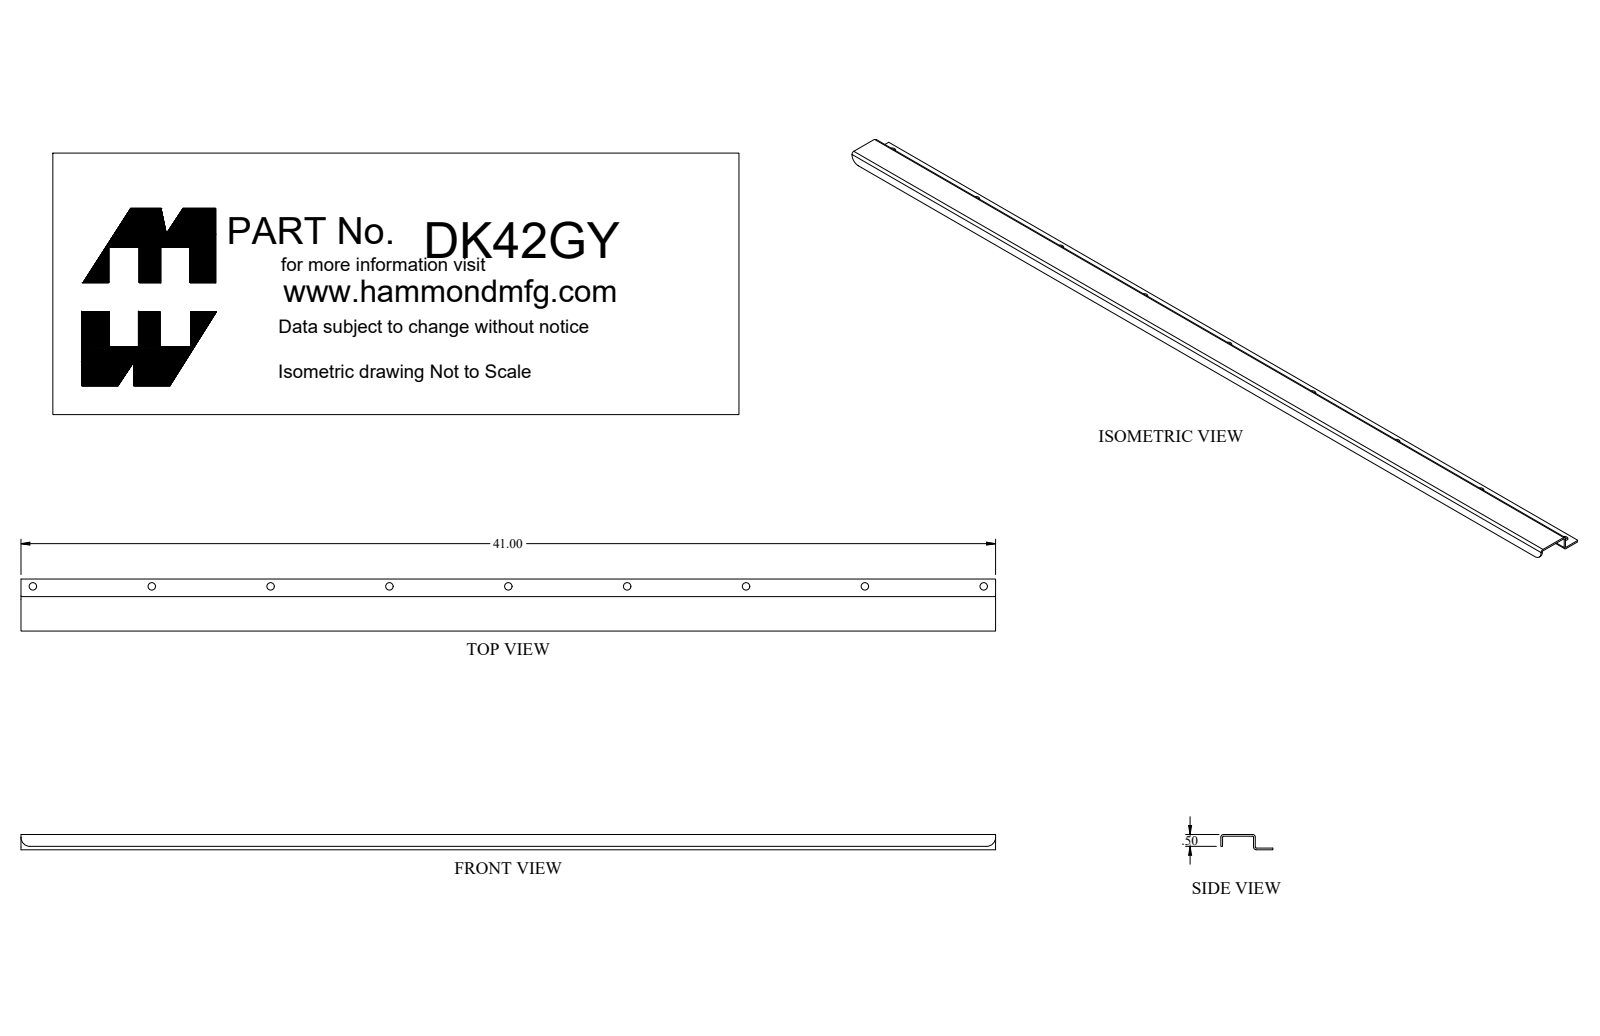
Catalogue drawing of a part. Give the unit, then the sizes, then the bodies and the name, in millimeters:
Units: millimetres
Overall size (bounding box): 1041.4 × 55.6 × 33.6
Round holes (diameter × count): ⌀8 ×9, ⌀5.1 ×1, ⌀7 ×1
Round bosses / shafts (diameter × count): ⌀15.9 ×1, ⌀12.3 ×1, ⌀6.4 ×1
Partial cylindrical surfaces — rounded edges, fillets, slot ends (radius × count): R0.9 ×3, R2.7 ×3, R9.5 ×2
Main face-to-face distances: 1.8, 14.5, 16.4, 35, 12.7, 1.6, 16.1, 18, 3.4, 36.8
Hole centre spacings: 127, 254, 381, 508, 635, 762, 889, 1016
Volume: 182 400 mm³ · Surface area: 212 100 mm²
Bodies: 5 solids, 77 faces (35 planar, 36 cylindrical, 6 other)
Part name (STEP PRODUCT): DK42GY_Default
STEP written by: SolidWorks 2018 (CONFIG_CONTROL_DESIGN)
